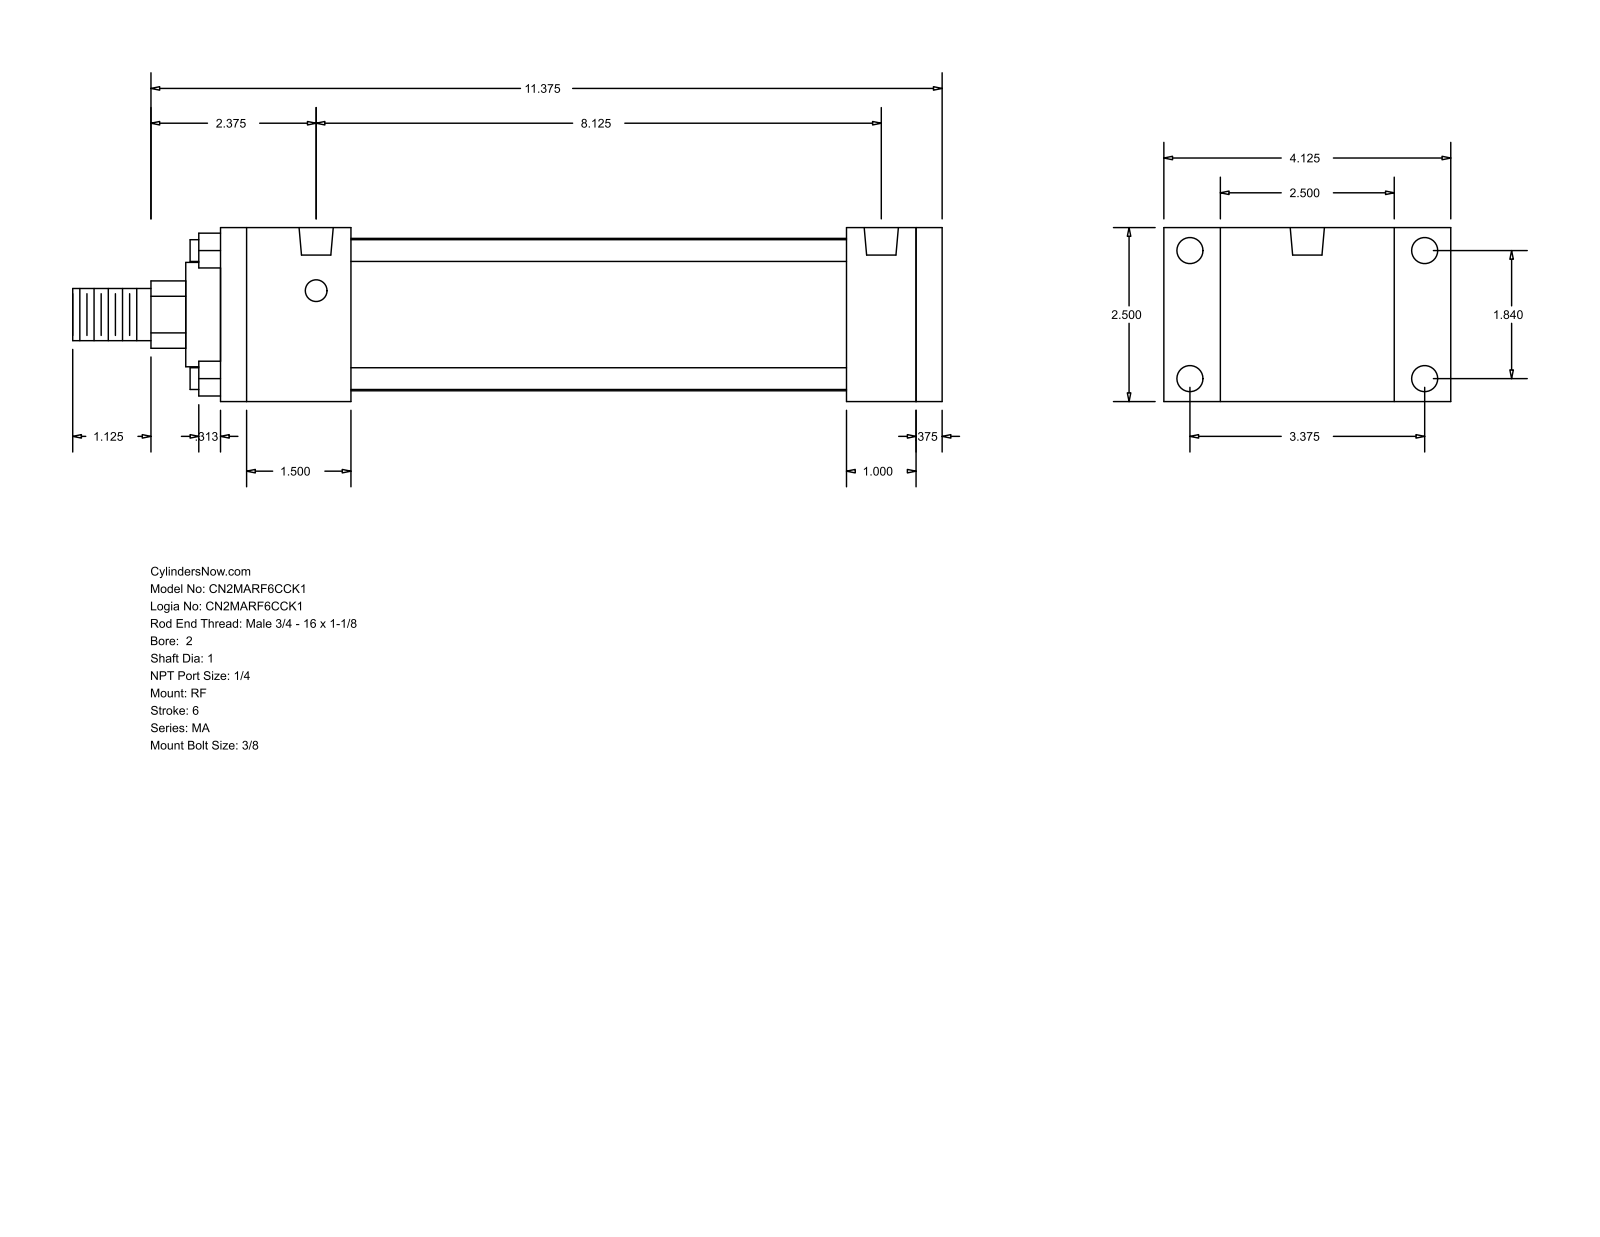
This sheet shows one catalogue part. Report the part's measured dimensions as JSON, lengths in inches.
{"part_name": "MA_RF__0200_1", "step_written_by": "GSSL Pune (CONFIG_CONTROL_DESIGN)", "units": "inches", "bodies": {"solids": 0, "faces": 92, "planar": 64, "cylindrical": 28, "other": 0}, "overall_size": [12.5, 4.125, 2.5], "round_holes": [[0.313, 4], [0.375, 4], [0.492, 2]], "round_bosses_or_shafts": [[0.313, 4], [2.19, 1], [1.5, 1], [1, 1], [0.75, 1]], "partial_cylinders_radius": [[0.484, 1]], "face_to_face_distances": [2.5, 10, 0.375, 10.375, 1, 0.813, 0.5, 1.875, 8.125, 8.5], "hole_center_spacings": [1.84, 3.375, 3.844, 8.125]}
